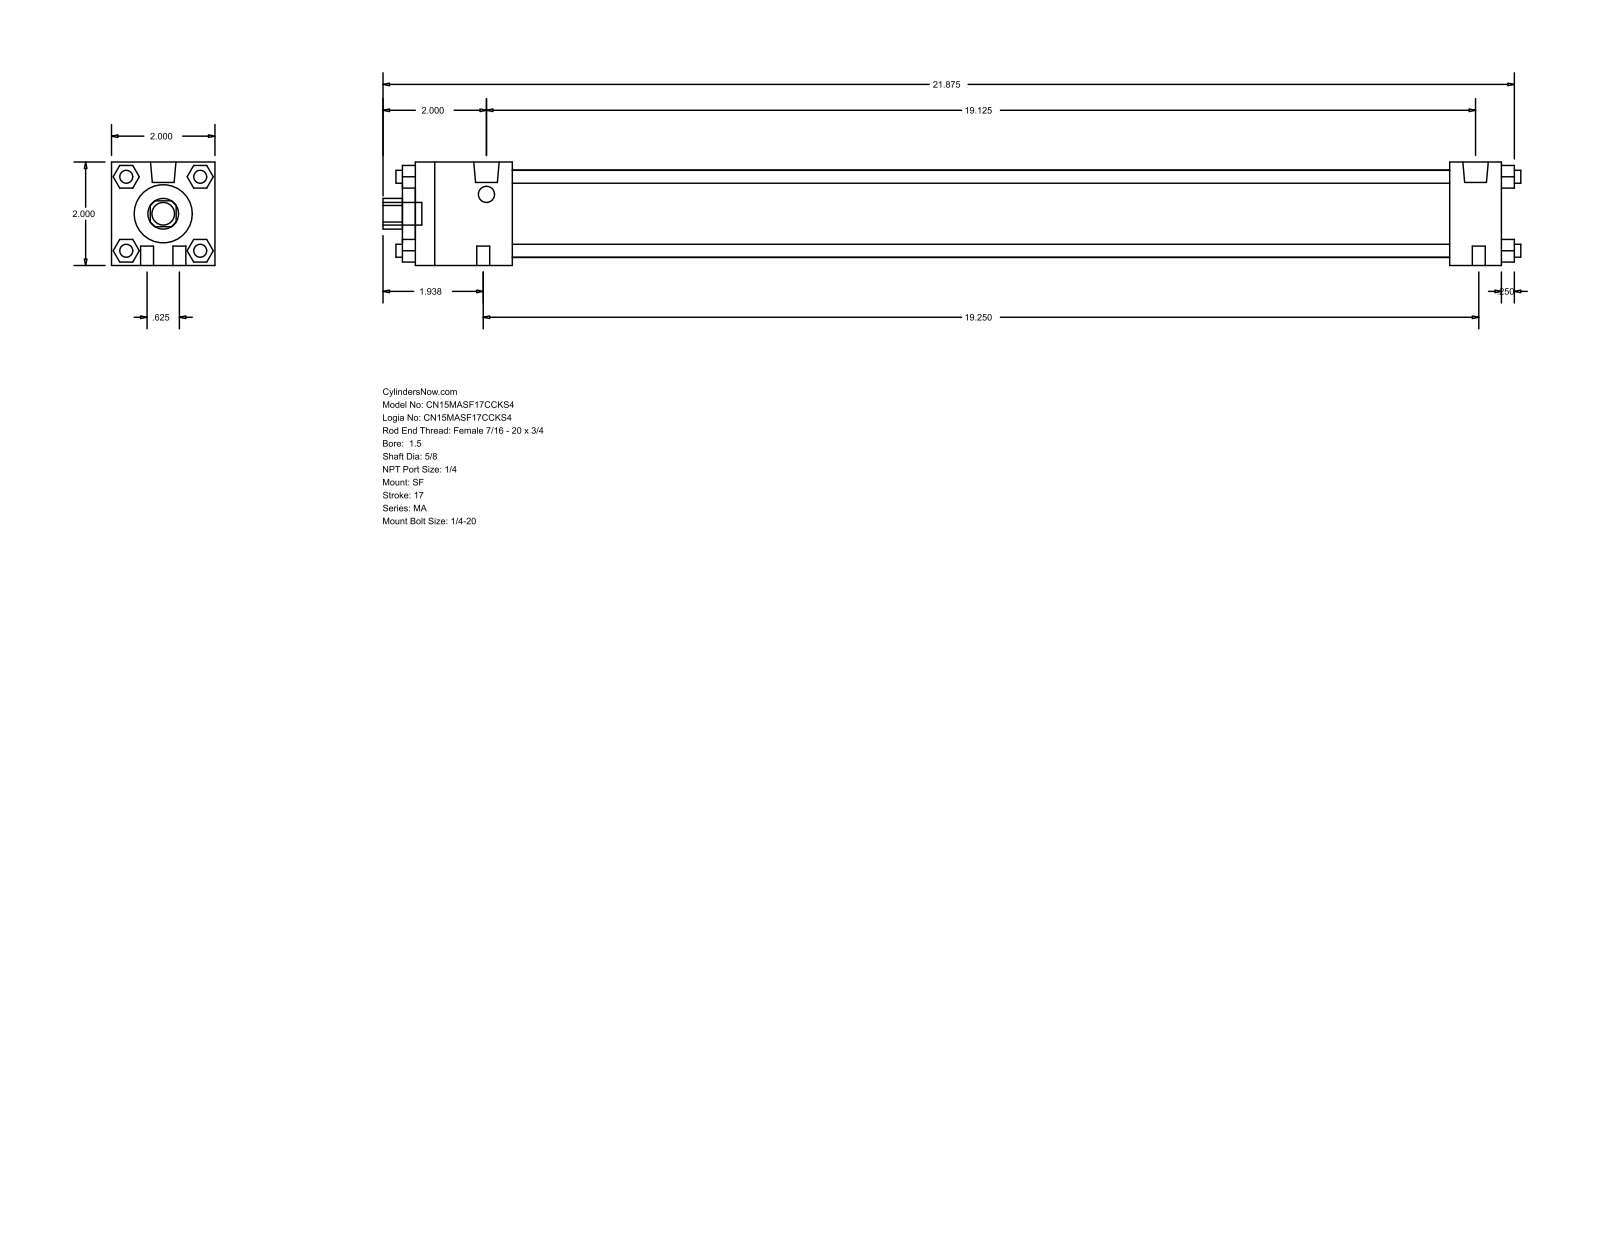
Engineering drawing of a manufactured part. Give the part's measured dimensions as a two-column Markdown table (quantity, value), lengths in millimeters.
| quantity | value |
| --- | --- |
| part name | MA_SF__0150_0.625 |
| STEP written by | GSSL Pune (CONFIG_CONTROL_DESIGN) |
| units | millimeters |
| bodies | 0 solids, 124 faces (94 planar, 30 cylindrical, 0 other) |
| overall size | 558.8 × 50.8 × 50.8 |
| round holes (diameter × count) | 15.88 × 1, 28.57 × 1, 42.93 × 1 |
| round bosses / shafts (diameter × count) | 6.35 × 8, 12.49 × 2, 7.94 × 2, 11.11 × 1 |
| partial cylindrical surfaces (radius × count) | 7.54 × 1 |
| main face-to-face distances | 50.8, 533.39, 6.35, 539.74, 47.62, 508, 460.38, 485.77, 25.39, 53.97 |
